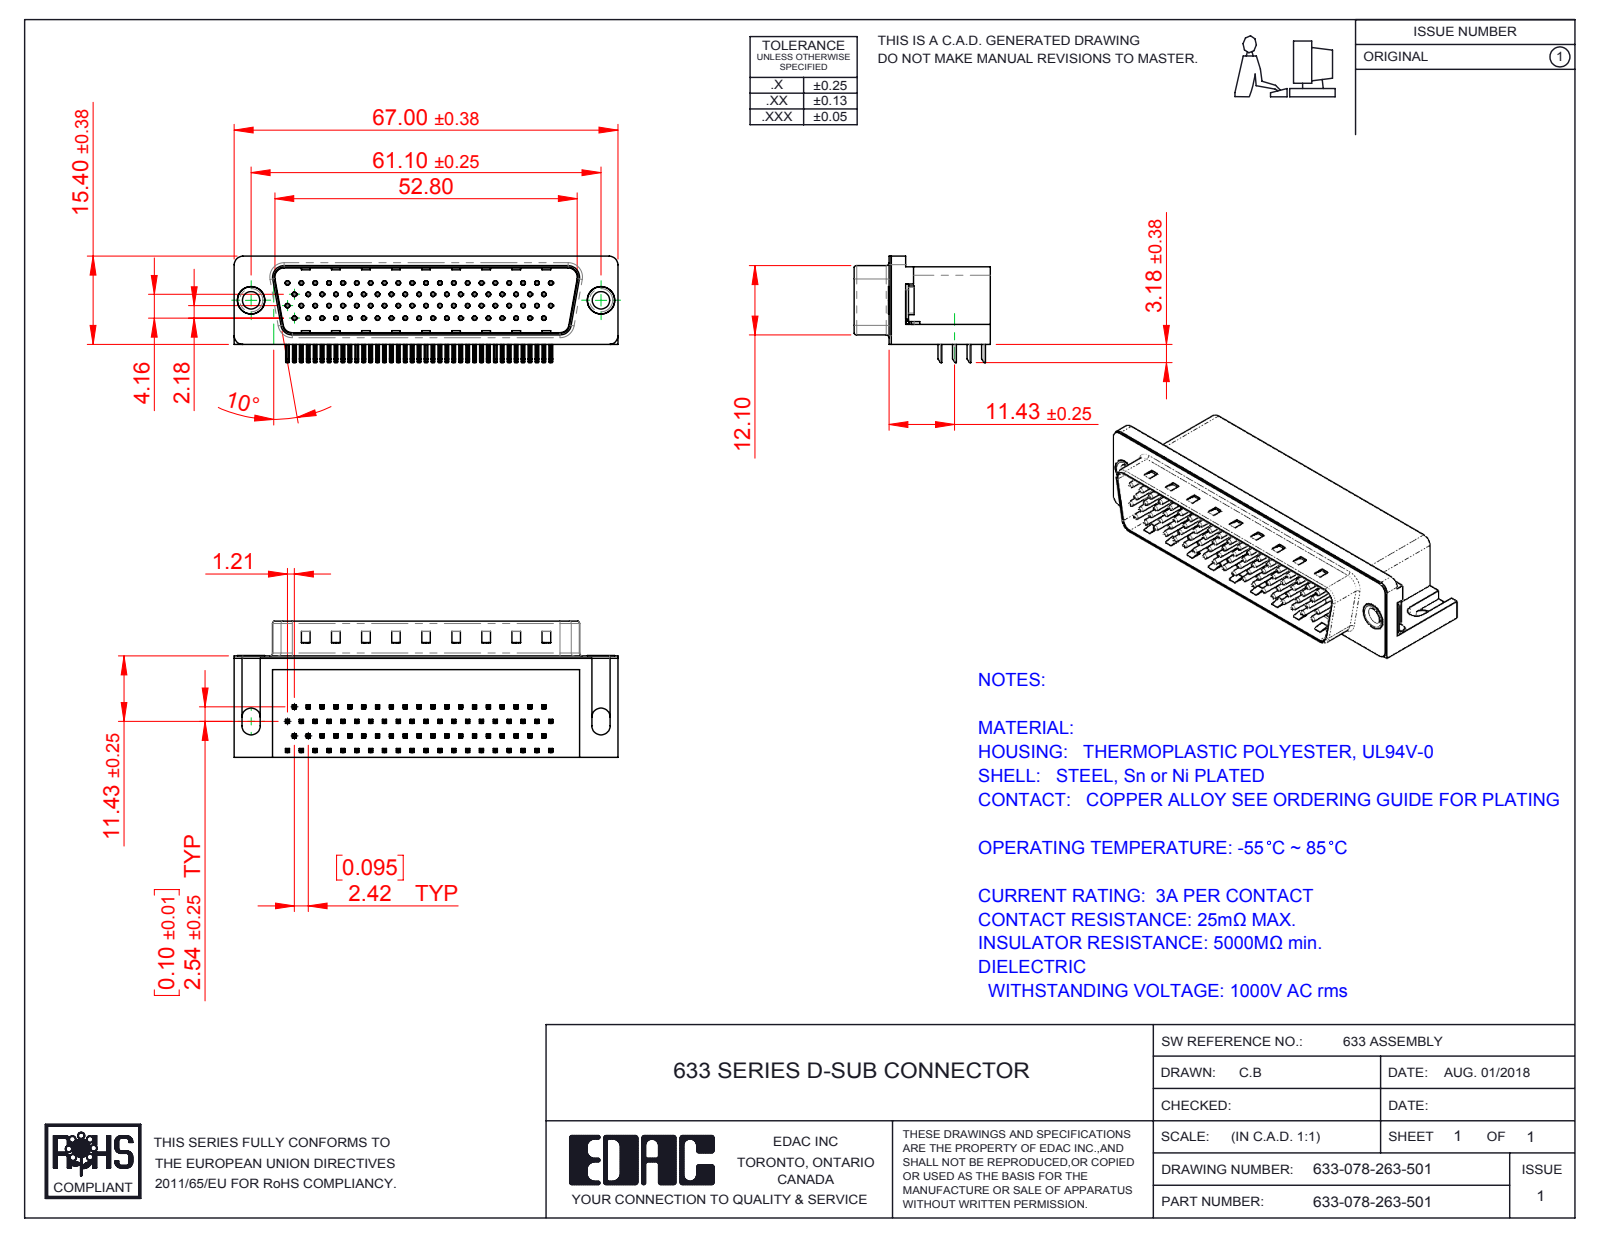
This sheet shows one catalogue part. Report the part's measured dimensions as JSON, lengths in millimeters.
{"part_name": "633 Non Board Mount_78 Contact; 633 Contact Top 78; 633 Contact Middle_78 Contact; 633 Contact Bottom_78 Contact (+5 more)", "step_written_by": "SolidWorks 2016 (CONFIG_CONTROL_DESIGN)", "units": "millimeters", "bodies": {"solids": 84, "faces": 6230, "planar": 3979, "cylindrical": 1756, "other": 495}, "overall_size": [67, 23.8, 18.58], "volume_mm3": 14553, "surface_area_mm2": 16106, "round_holes": [[0.35, 78], [0.8, 78], [3.05, 2], [4, 2], [4.8, 2], [5, 2]], "round_bosses_or_shafts": [[0.75, 78], [4.9, 2], [4.75, 2], [3.85, 2]], "partial_cylinders_radius": [[0.25, 320], [0.12, 156], [1, 16], [0.5, 9], [1.6, 8], [1.5, 6], [0.45, 4], [0.9, 4]], "face_to_face_distances": [0.4, 13.2, 17.3, 11.7, 13.35, 2.05, 13.75, 1.65, 11.9, 1.85], "hole_center_spacings": [2.42, 4.84, 7.26, 9.68, 6.26, 7.13, 12.1, 8.62]}
